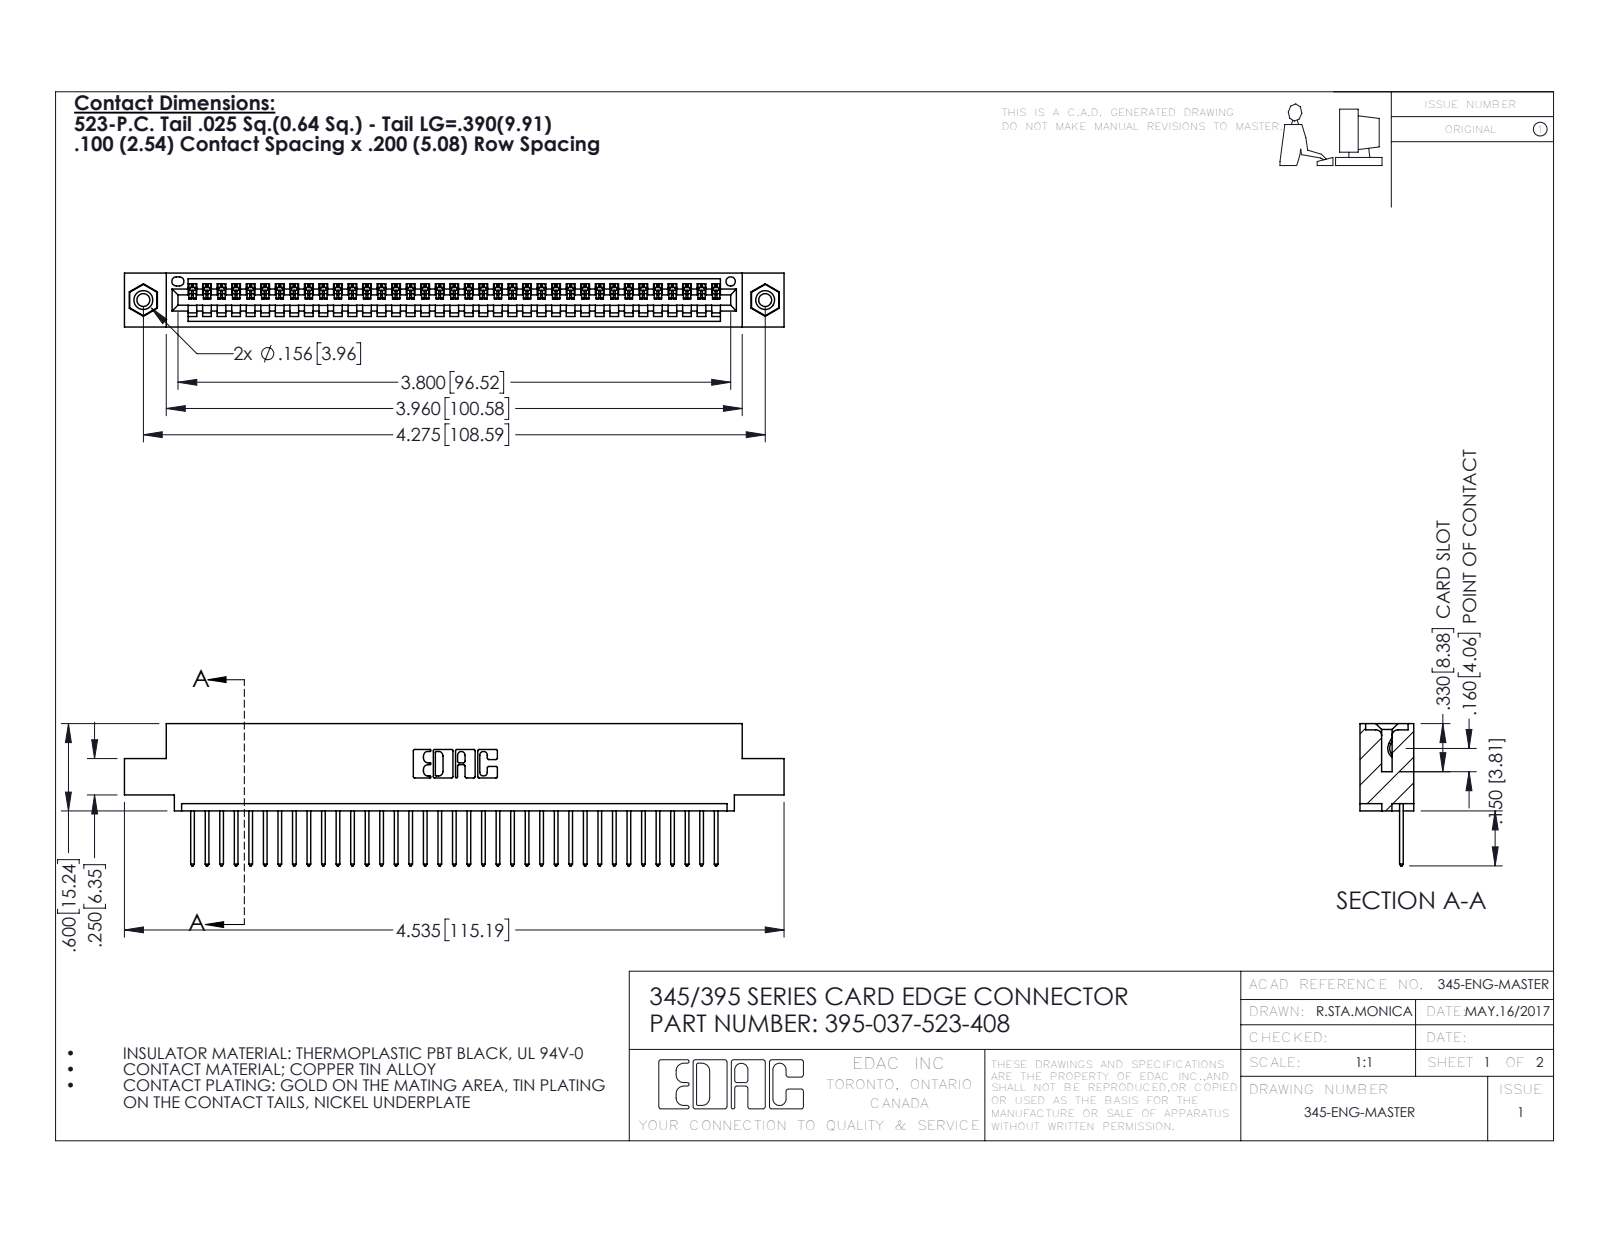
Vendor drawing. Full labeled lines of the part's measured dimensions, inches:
Part name (STEP PRODUCT): 345 Part_0.110 Offset - 0.156 Dia-TI; 395-037-523-408; 345-250-001_345-250-003-102; 345-292-001_345-293-123
STEP written by: SolidWorks 2016 (CONFIG_CONTROL_DESIGN)
Units: inches
Bodies: 40 solids, 2336 faces (1596 planar, 724 cylindrical, 16 other)
Overall size (bounding box): 4.535 × 0.977 × 0.37
Volume: 0.659 in³ · Surface area: 22.37 in²
Round holes (diameter × count): ⌀0.089 ×2, ⌀0.125 ×2, ⌀0.156 ×2, ⌀0.064 ×1
Round bosses / shafts (diameter × count): ⌀0.155 ×2
Partial cylindrical surfaces — rounded edges, fillets, slot ends (radius × count): R0.006 ×74, R0.01 ×74, R0.01 ×22, R0.007 ×6, R0.031 ×6, R0.026 ×3, R0.031 ×2, R0.04 ×2
Main face-to-face distances: 0.072, 0.298, 0.37, 0.2, 0.098, 0.272, 0.025, 0.225, 0.149, 0.072
Hole centre spacings: 0.27, 4.039, 4.275
